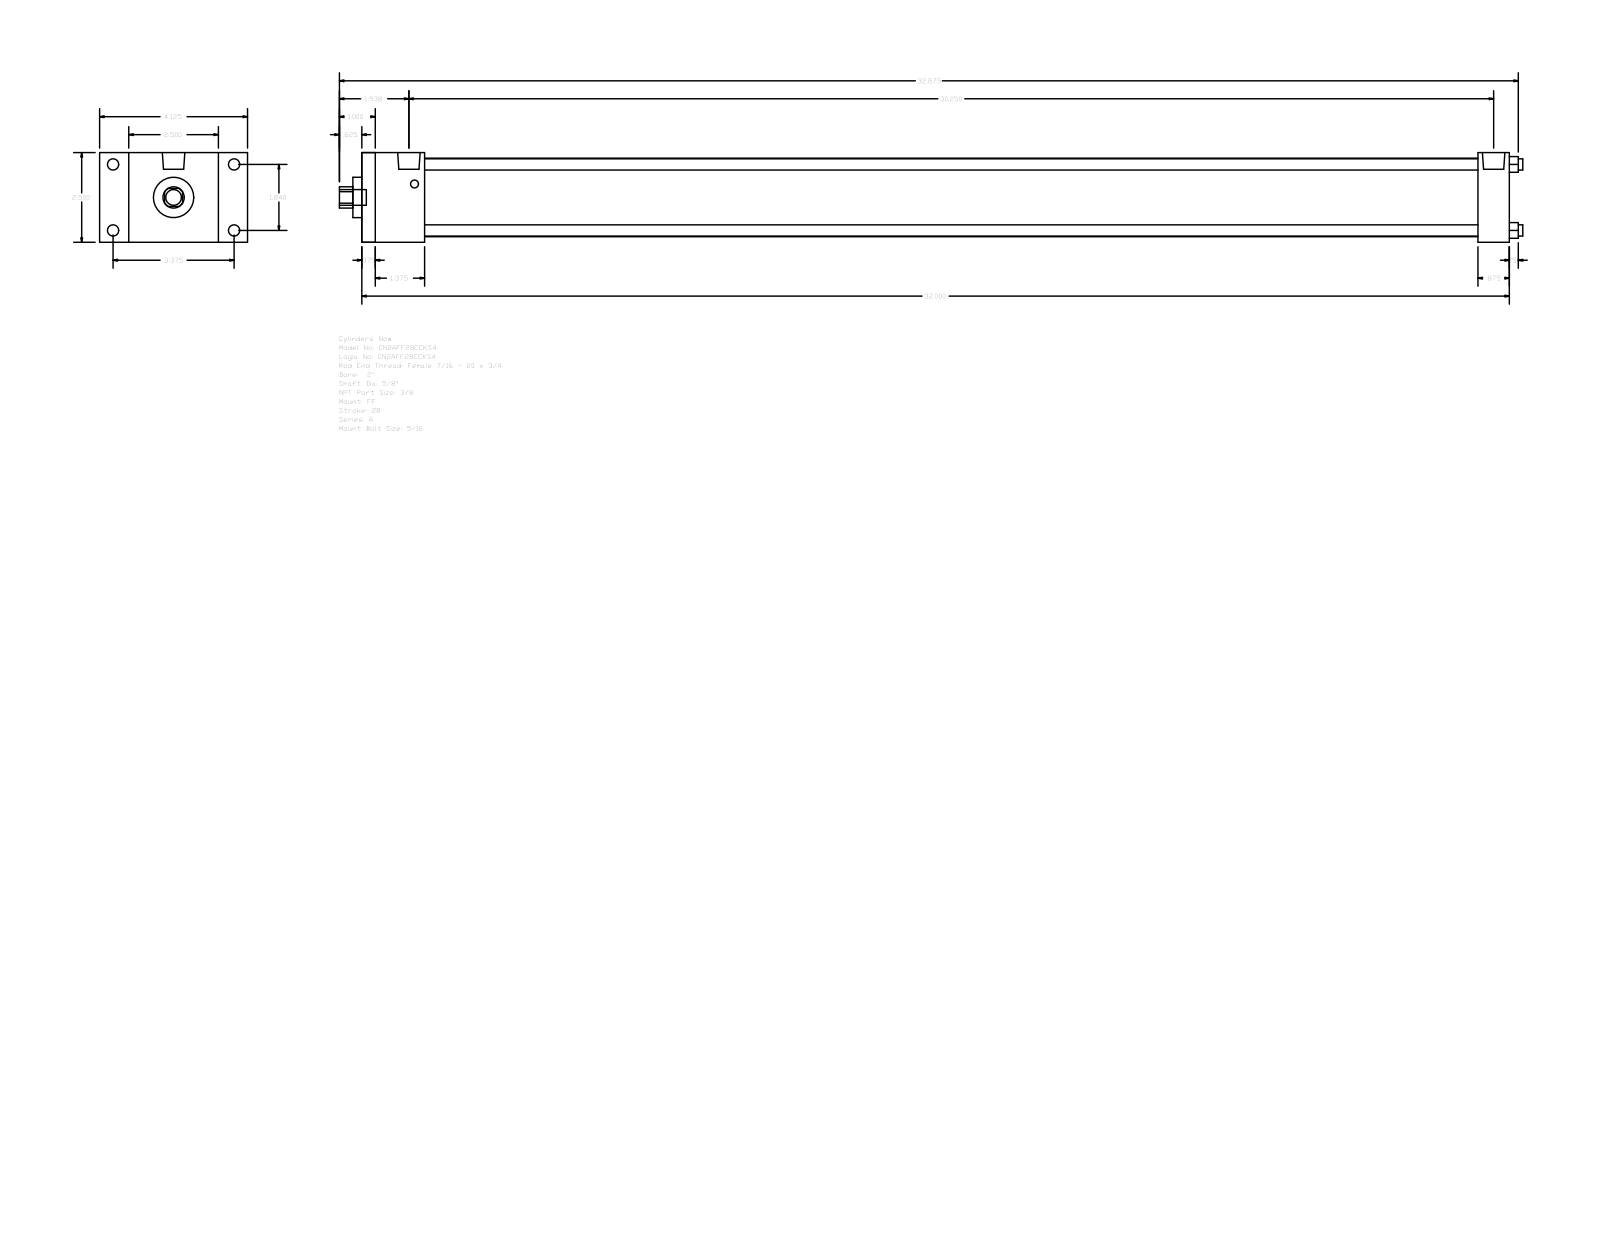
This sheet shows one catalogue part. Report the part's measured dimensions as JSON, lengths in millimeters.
{"part_name": "A_FF__0200_0.625", "step_written_by": "GSSL Pune (CONFIG_CONTROL_DESIGN)", "units": "millimeters", "bodies": {"solids": 0, "faces": 92, "planar": 64, "cylindrical": 28, "other": 0}, "overall_size": [838.2, 104.78, 63.5], "round_holes": [[7.94, 4], [15.88, 1], [28.57, 1], [55.63, 1]], "round_bosses_or_shafts": [[7.94, 4], [5.56, 4], [15.93, 2], [11.11, 1]], "partial_cylinders_radius": [[7.54, 1]], "face_to_face_distances": [63.5, 812.79, 9.52, 803.27, 44.45, 790.57, 34.93, 781.05, 746.12, 768.34], "hole_center_spacings": [33.05, 46.74, 66.1]}
